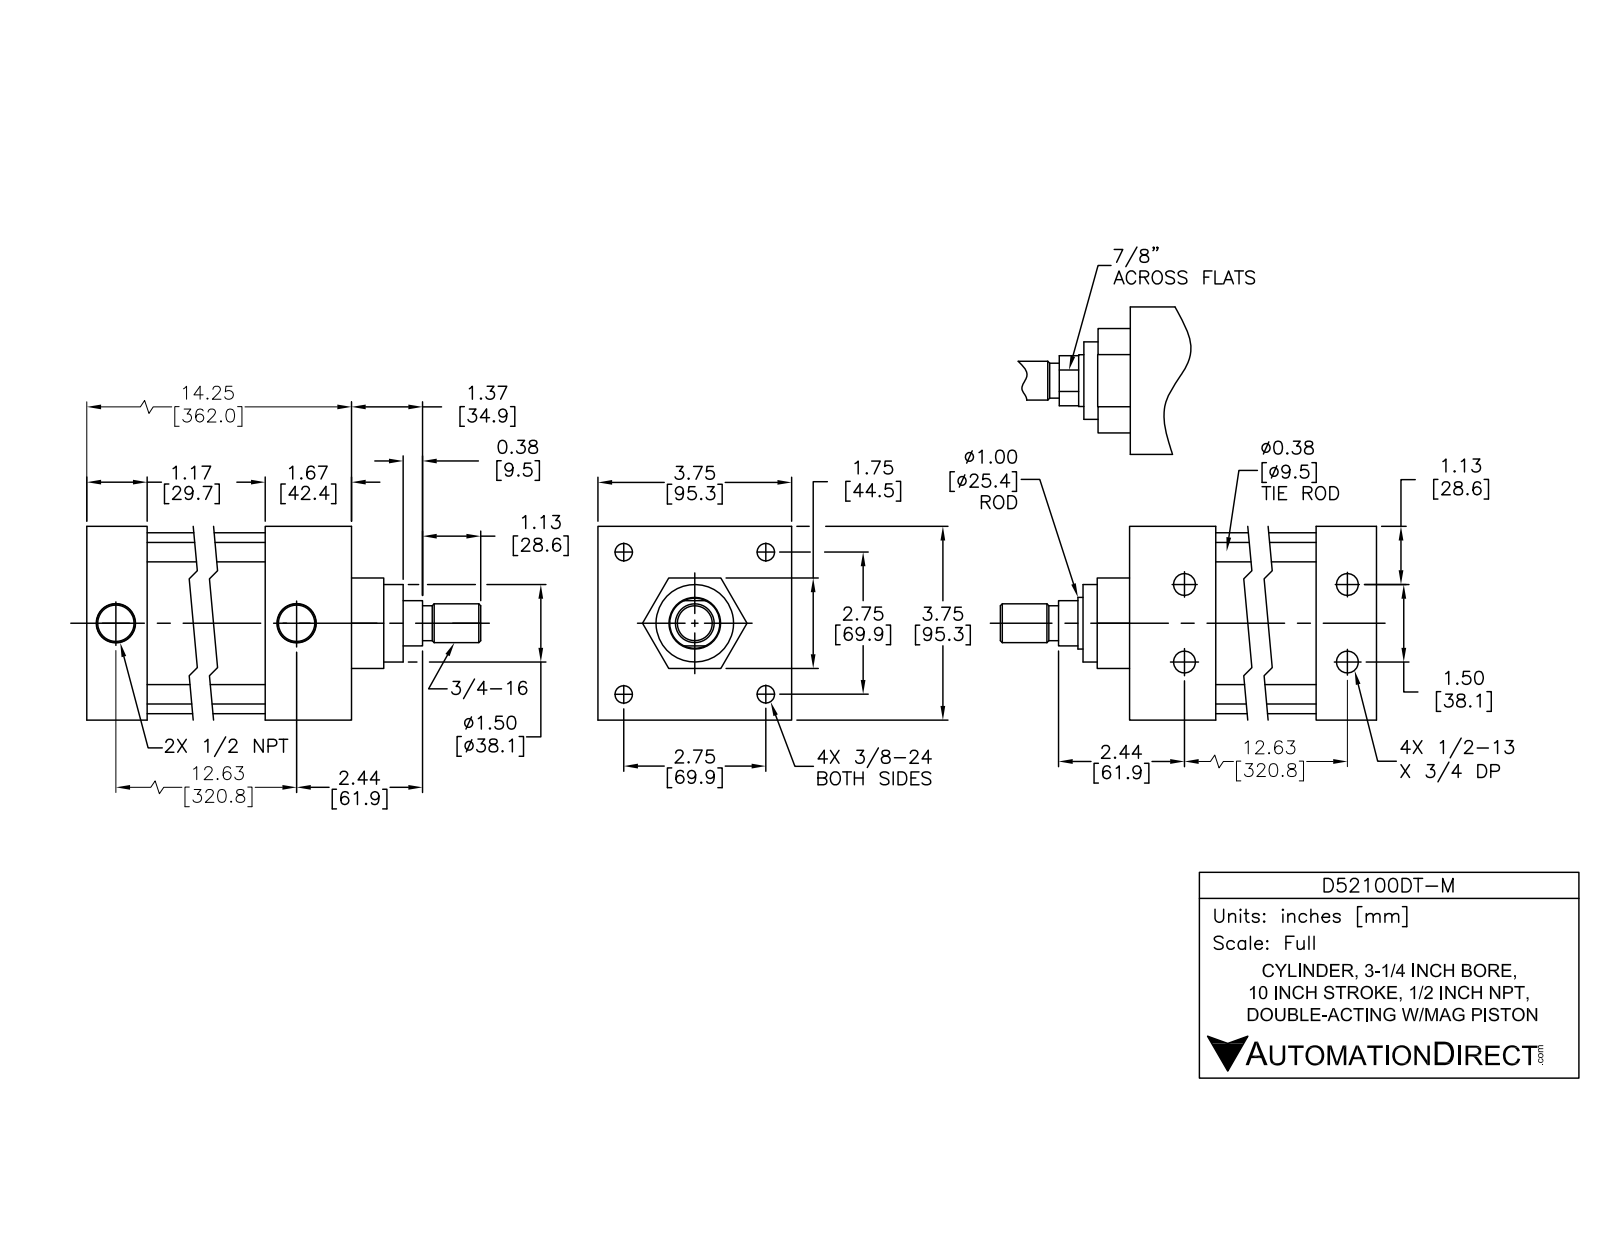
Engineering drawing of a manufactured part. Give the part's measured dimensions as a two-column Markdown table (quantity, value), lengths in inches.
| quantity | value |
| --- | --- |
| part name | D52100DT-M; D52100DT-M BODY; D52100DT-M PISTON |
| STEP written by | SolidWorks 2015 (AUTOMOTIVE_DESIGN) |
| units | inches |
| bodies | 12 solids, 303 faces (99 planar, 114 cylindrical, 90 other) |
| overall size | 16.745 × 3.75 × 3.75 |
| volume | 78.52 in³ |
| surface area | 523.2 in² |
| round holes (diameter × count) | 0.33 × 4, 0.406 × 4, 0.417 × 4, 0.625 × 4, 0.5 × 2, 0.766 × 2, 1 × 1, 1.003 × 1, 3.25 × 1 |
| round bosses / shafts (diameter × count) | 0.609 × 4, 0.375 × 4, 0.34 × 4, 3.5 × 1, 3.247 × 1, 1.75 × 1, 0.997 × 1, 0.97 × 1 |
| partial cylindrical surfaces (radius × count) | 0.375 × 4 |
| main face-to-face distances | 3.75, 0.08, 11.326, 14.246, 1.75, 12.997, 1.249, 11.751, 1.246, 2.495 |
| hole center spacings | 2.758, 1.95, 0.75, 0.76, 1.5, 3.9, 12.5, 12.526 |
